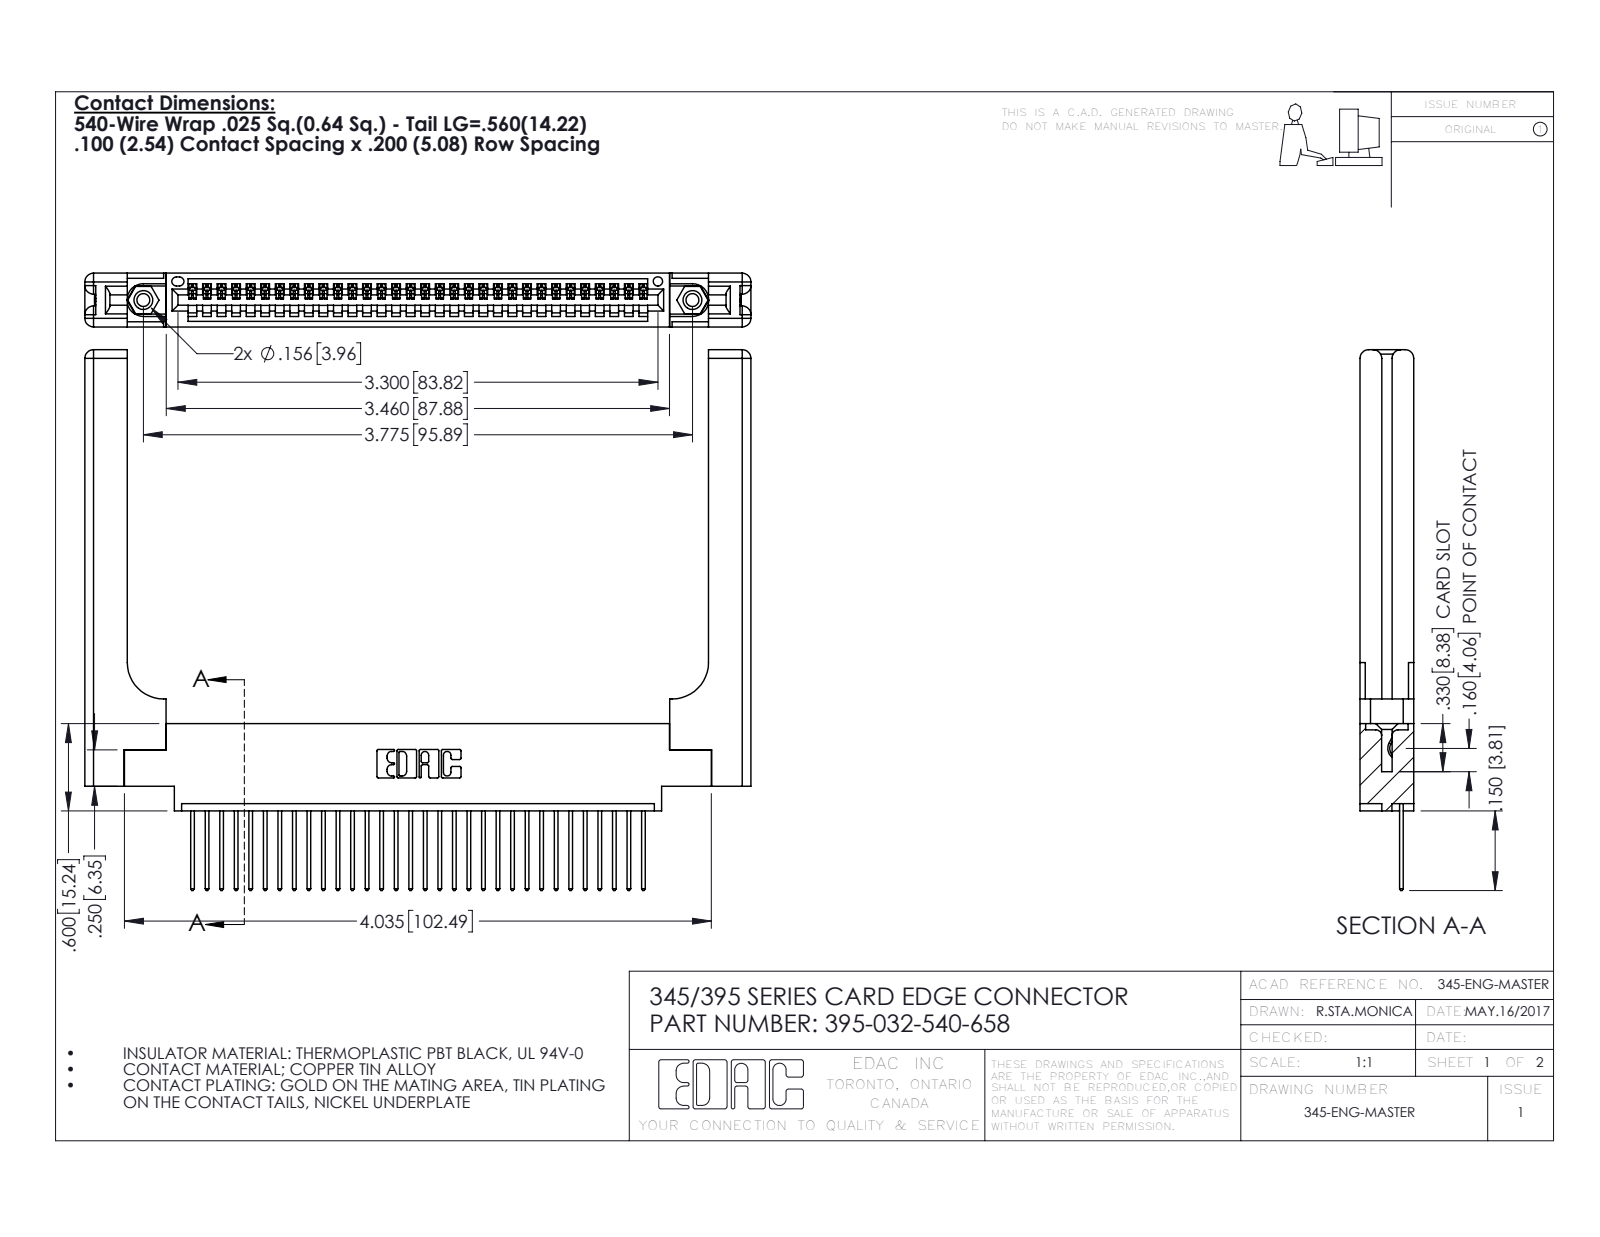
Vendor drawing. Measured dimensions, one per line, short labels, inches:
name: 345-220-058_345-220-058; 345-292-001_345-293-140; 345-250-001_345-250-001-102; 395-032-540-658 (+1 more)
written by: SolidWorks 2016 (CONFIG_CONTROL_DESIGN)
unit: in
bodies: 37 solids, 2242 faces (1512 planar, 670 cylindrical, 60 other)
size: 4.579 × 3.717 × 0.37
volume: 1.184 in³; area: 31.13 in²
holes: 2× ⌀0.089, 2× ⌀0.125, 2× ⌀0.156, 1× ⌀0.064
bosses: 2× ⌀0.155
rounds: 64× R0.006, 64× R0.01, 22× R0.01, 16× R0.06, 6× R0.007, 6× R0.031, 3× R0.026, 2× R0.03
face distances: 0.37, 0.072, 0.298, 0.098, 0.272, 0.025, 0.2, 0.148, 0.15, 0.077
hole spacings: 0.27, 3.54, 3.775
